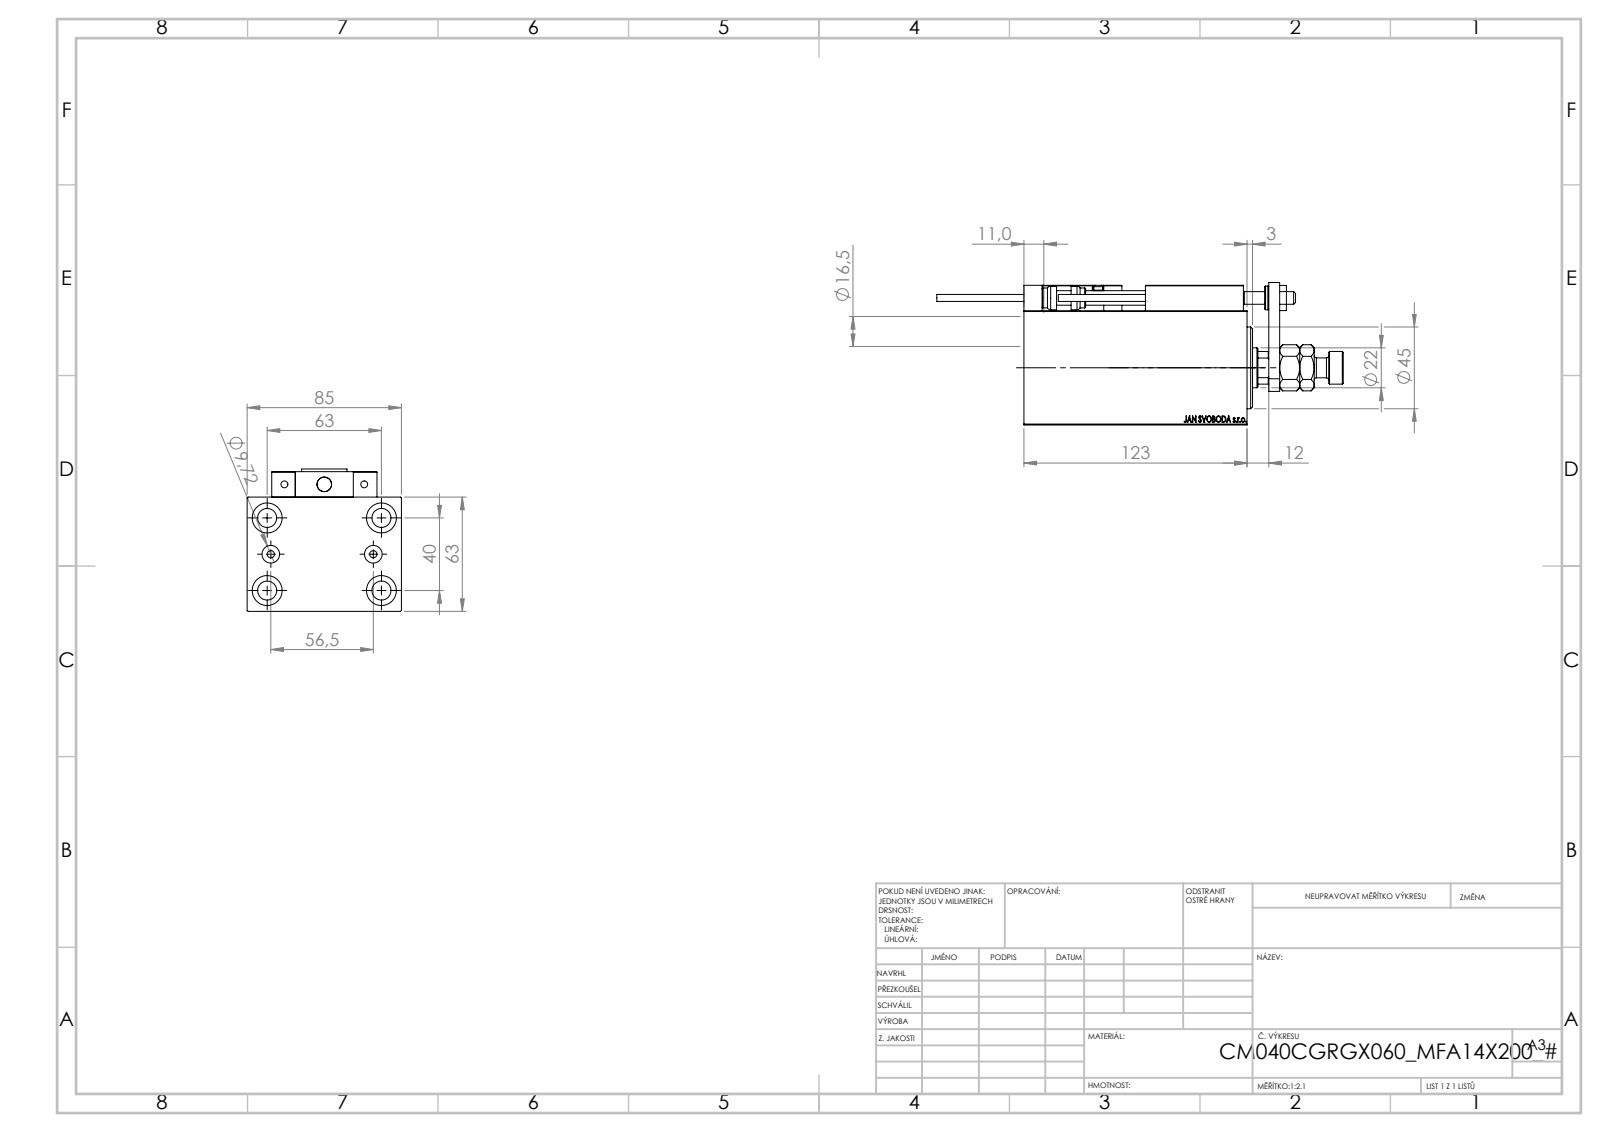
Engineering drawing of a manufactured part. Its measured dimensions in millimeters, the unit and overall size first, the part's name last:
Units: millimetres
Overall size (bounding box): 224 × 85 × 78.5
Round holes (diameter × count): ⌀4 ×6, ⌀8 ×5, ⌀16.5 ×5, ⌀3.2 ×4, ⌀10.5 ×4, ⌀5 ×2, ⌀9.72 ×2, ⌀7 ×1, ⌀12.5 ×1, ⌀22 ×1, ⌀25.5 ×1, ⌀40 ×1
Round bosses / shafts (diameter × count): ⌀11 ×2, ⌀5 ×2, ⌀3.8 ×2, ⌀18 ×1, ⌀13 ×1
Partial cylindrical surfaces — rounded edges, fillets, slot ends (radius × count): R0.3 ×30, R3 ×2, R10.5 ×1
Main face-to-face distances: 63, 85, 12, 111, 123, 14, 18, 30, 77, 20
Hole centre spacings: 37.31, 11.37, 20, 20.1, 20.5, 29.59, 29.69, 36.06
Volume: 614 041 mm³ · Surface area: 129 770 mm²
Bodies: 24 solids, 1330 faces (576 planar, 188 cylindrical, 566 other)
Part name (STEP PRODUCT): SWITCH DIM B,W; V450CM_C_VCP; TYC_L79; MAGNET (+7 more)
STEP written by: SolidWorks 2019 (CONFIG_CONTROL_DESIGN)
